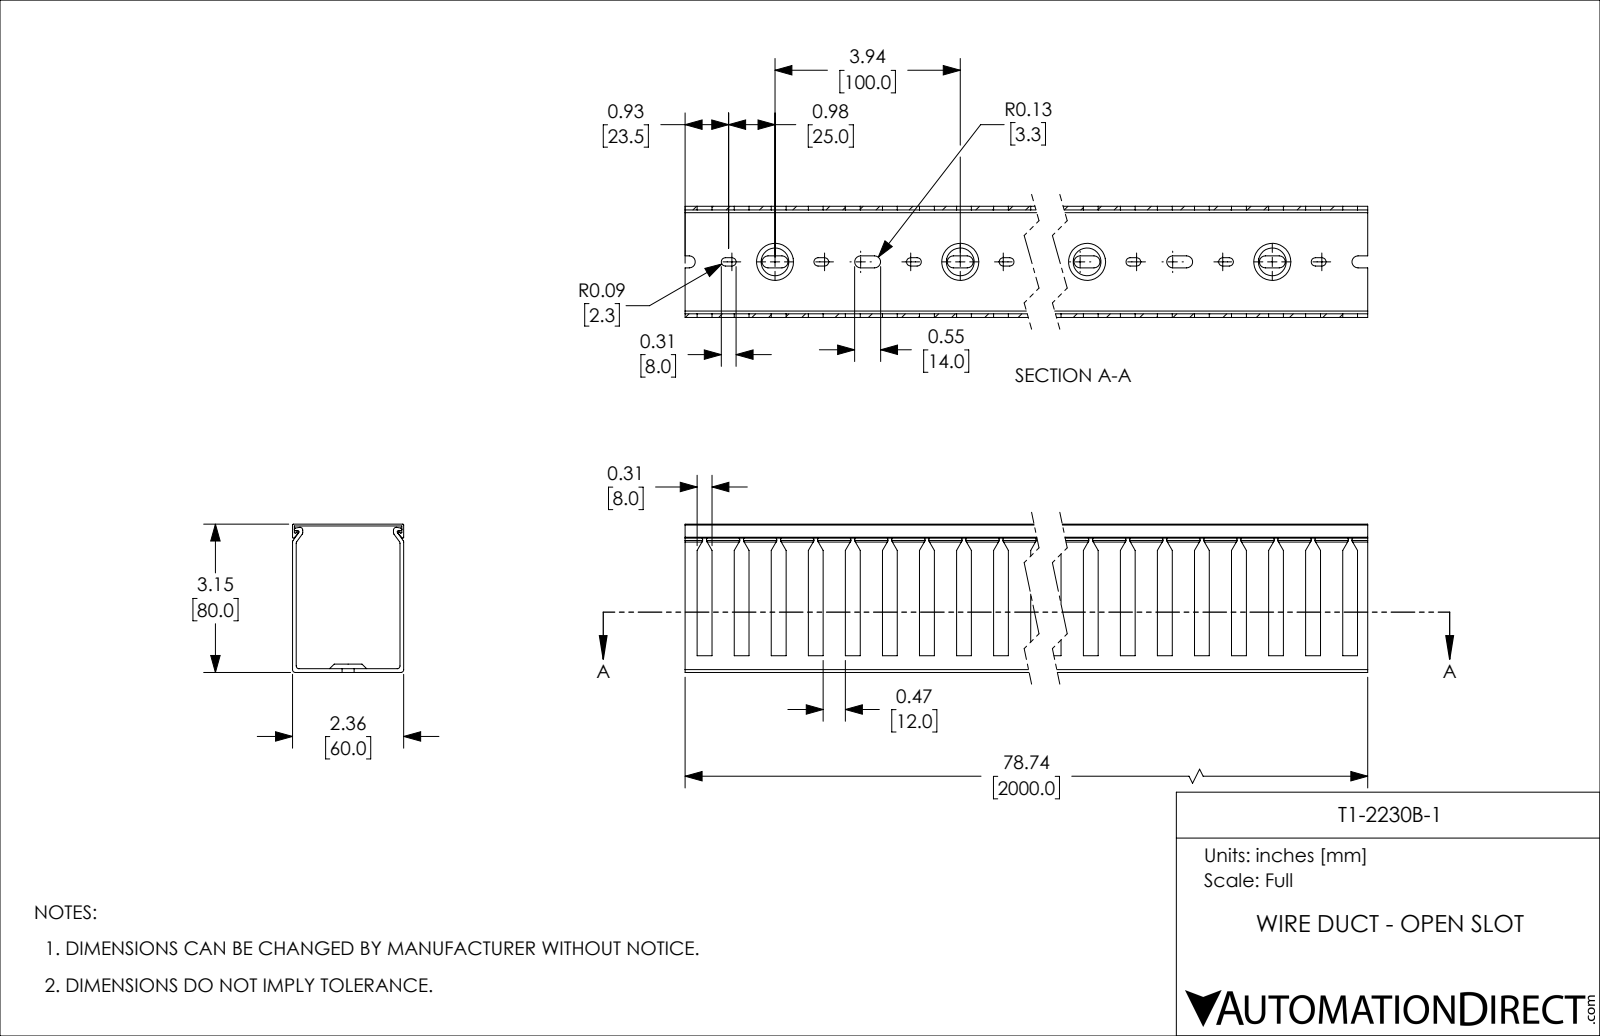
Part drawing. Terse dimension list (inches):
name: T1-2230B-1
written by: SolidWorks 2021 (CONFIG_CONTROL_DESIGN)
unit: in
bodies: 2 solids, 1005 faces (534 planar, 431 cylindrical, 40 other)
size: 78.74 × 3.15 × 2.362
volume: 61.51 in³; area: 1 809 in²
rounds: 80× R0.089, 80× R0.128, 12× R0.059, 8× R0.02, 6× R0.03
face distances: 0.079, 2.283, 2.362, 0.039, 2.205, 3.15, 3.11, 3.031, 3.071, 2.323
